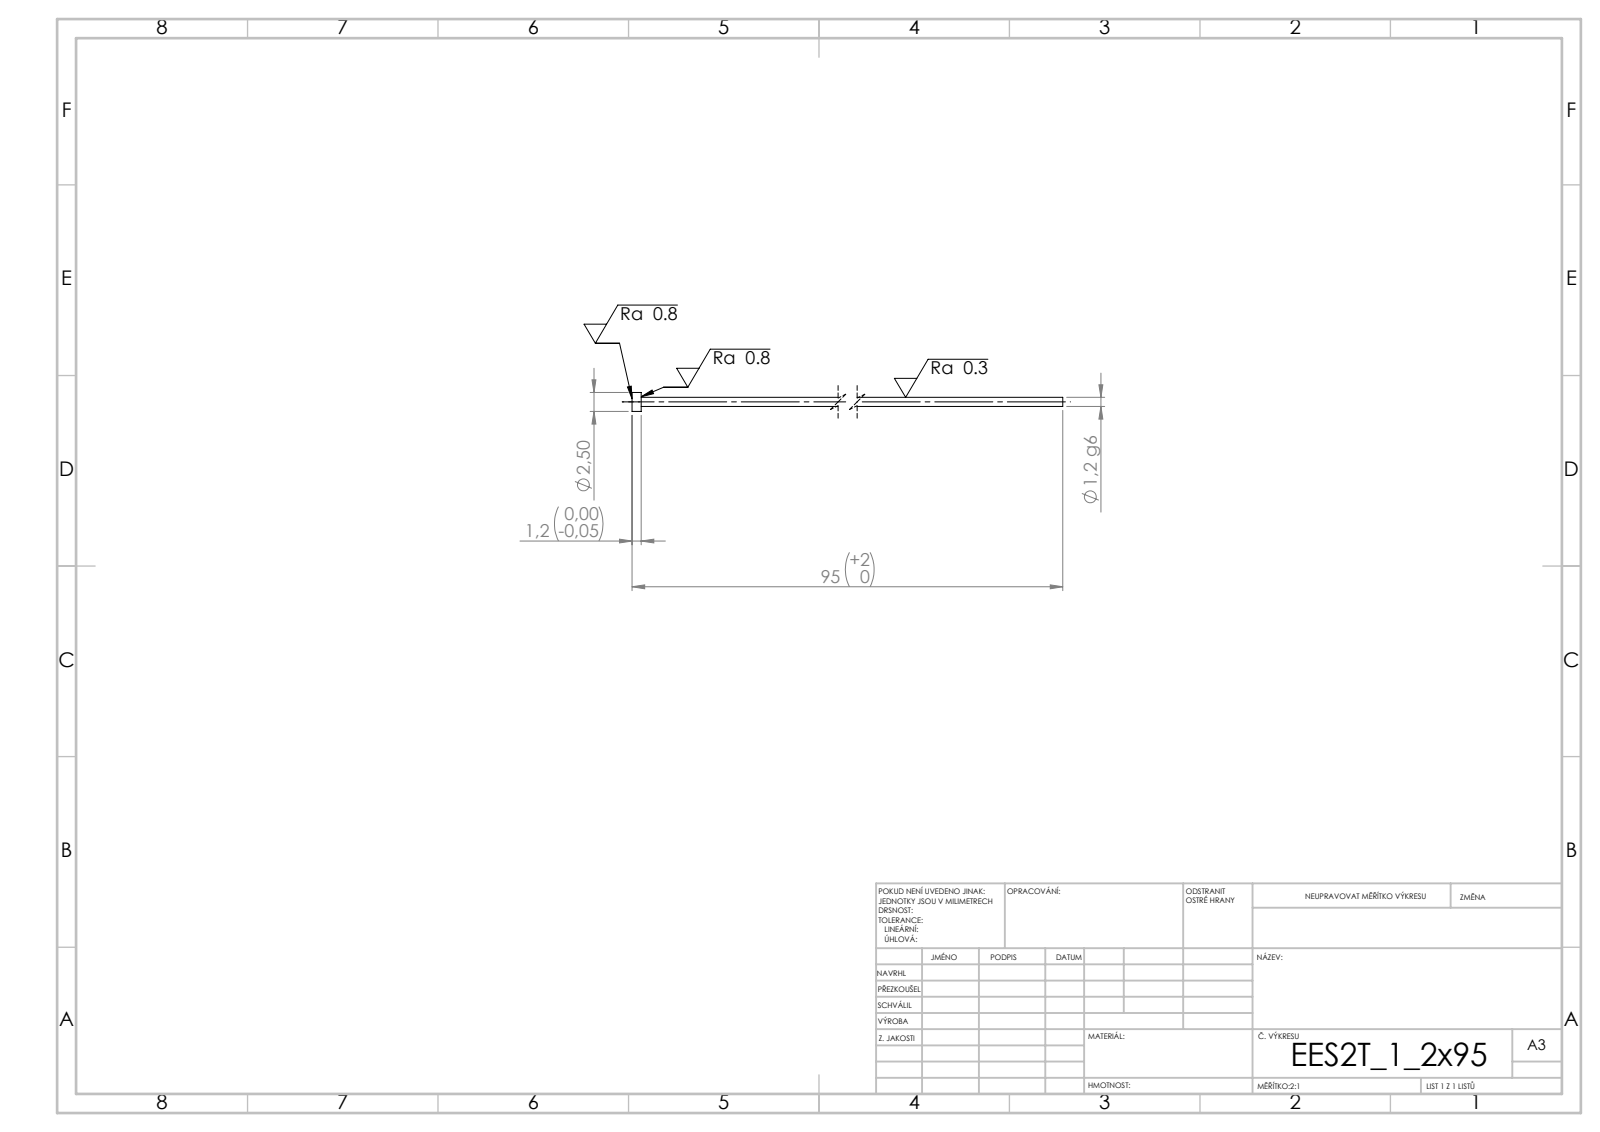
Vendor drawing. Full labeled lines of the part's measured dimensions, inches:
STEP written by: SolidWorks 2019 (CONFIG_CONTROL_DESIGN)
Units: inches
Bodies: 1 solid, 7 faces (3 planar, 4 cylindrical, 0 other)
Overall size (bounding box): 3.74 × 0.098 × 0.098
Volume: 0.007 in³ · Surface area: 0.578 in²
Round bosses / shafts (diameter × count): ⌀0.098 ×1, ⌀0.047 ×1
Main face-to-face distances: 0.047, 3.74, 3.693
